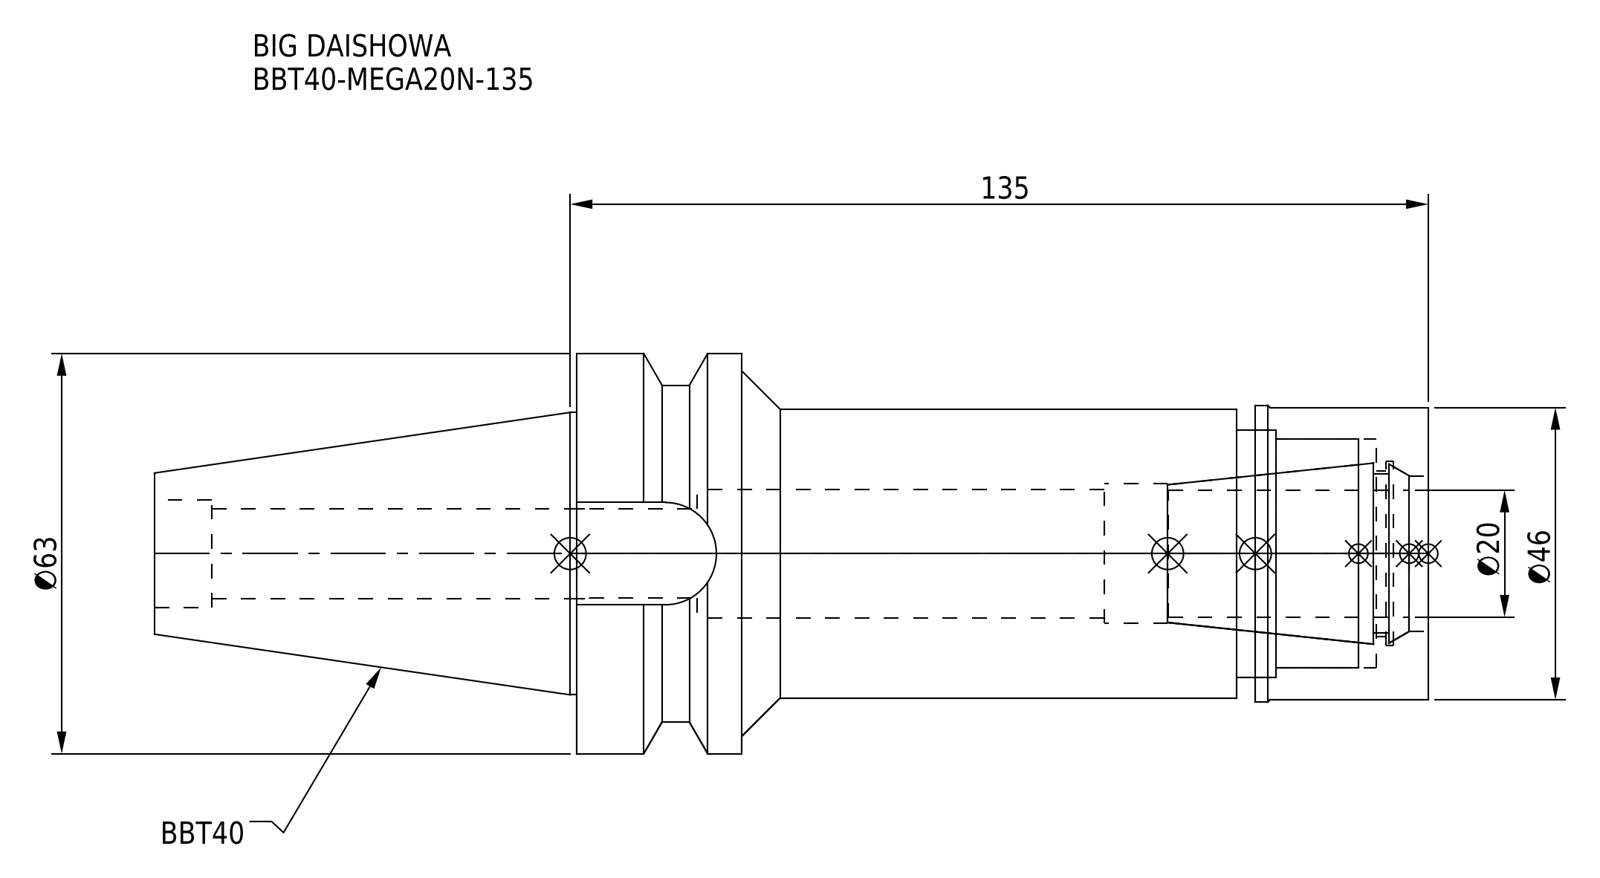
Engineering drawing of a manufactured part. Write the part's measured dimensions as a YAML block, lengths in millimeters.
part_name: "MGN20_1.stp; BBT40MN20135-200_ASM.stp; BBT40-MEGA20N-135-200.stp; BBT40-MEGA20N-135-200-FreeParts (+3 more)"
step_written_by: "SolidWorks 2019 (CONFIG_CONTROL_DESIGN)"
units: millimeters
bodies: {solids: 2, faces: 80, planar: 24, cylindrical: 42, other: 14}
overall_size: [200.4, 63, 63]
volume: 253399
surface_area: 51586
round_holes:
  - {diameter: 14, count: 1}
  - {diameter: 14.1, count: 1}
  - {diameter: 14.2, count: 1}
  - {diameter: 17, count: 1}
  - {diameter: 20.3, count: 1}
  - {diameter: 22, count: 1}
  - {diameter: 24.5, count: 1}
  - {diameter: 26, count: 1}
  - {diameter: 29, count: 1}
  - {diameter: 36, count: 1}
  - {diameter: 39, count: 1}
round_bosses_or_shafts:
  - {diameter: 63, count: 1}
  - {diameter: 53, count: 1}
  - {diameter: 46.7, count: 1}
  - {diameter: 46, count: 1}
  - {diameter: 45.5, count: 1}
  - {diameter: 44.45, count: 1}
partial_cylinders:
  - {radius: 8.05, count: 1}
face_to_face_distances: [134, 106.8, 19, 108, 26, 27.2, 80.8, 8.2, 99.8, 125.8]
